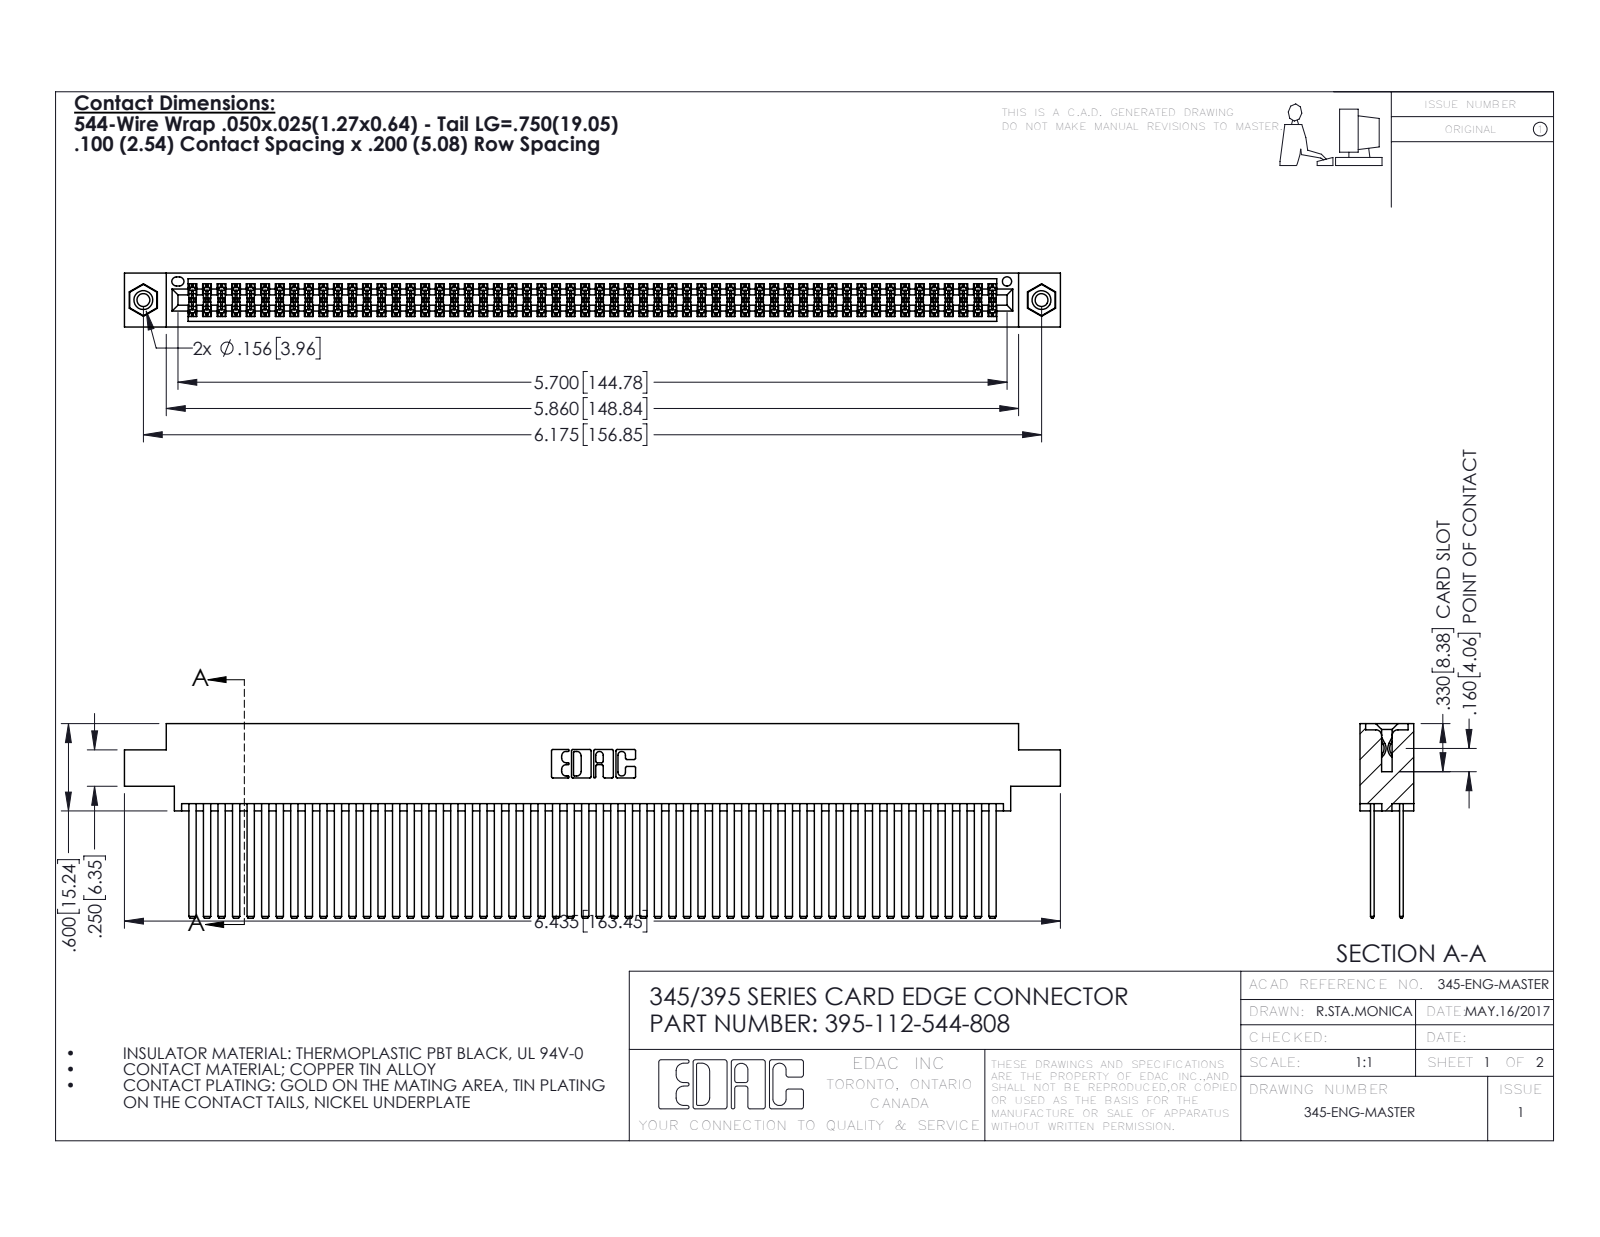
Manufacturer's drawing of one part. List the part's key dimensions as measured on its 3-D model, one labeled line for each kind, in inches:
Part name (STEP PRODUCT): 345-250-001_345-250-003-102; 395-112-544-808; 345 Part_0.170 Offset - 0.156 Dia-TI; 345-292-001_345-293-144
STEP written by: SolidWorks 2016 (CONFIG_CONTROL_DESIGN)
Units: inches
Bodies: 115 solids, 5118 faces (3364 planar, 1738 cylindrical, 16 other)
Overall size (bounding box): 6.435 × 1.337 × 0.37
Volume: 1.065 in³ · Surface area: 47.79 in²
Round holes (diameter × count): ⌀0.089 ×2, ⌀0.125 ×2, ⌀0.156 ×2, ⌀0.064 ×1
Round bosses / shafts (diameter × count): ⌀0.155 ×2
Partial cylindrical surfaces — rounded edges, fillets, slot ends (radius × count): R0.006 ×168, R0.01 ×22, R0.007 ×6, R0.031 ×6, R0.026 ×3, R0.014 ×2, R0.019 ×2, R0.022 ×2
Main face-to-face distances: 0.2, 0.025, 0.072, 0.098, 0.272, 0.298, 0.225, 0.175, 0.37, 0.15
Hole centre spacings: 0.27, 5.939, 6.175
